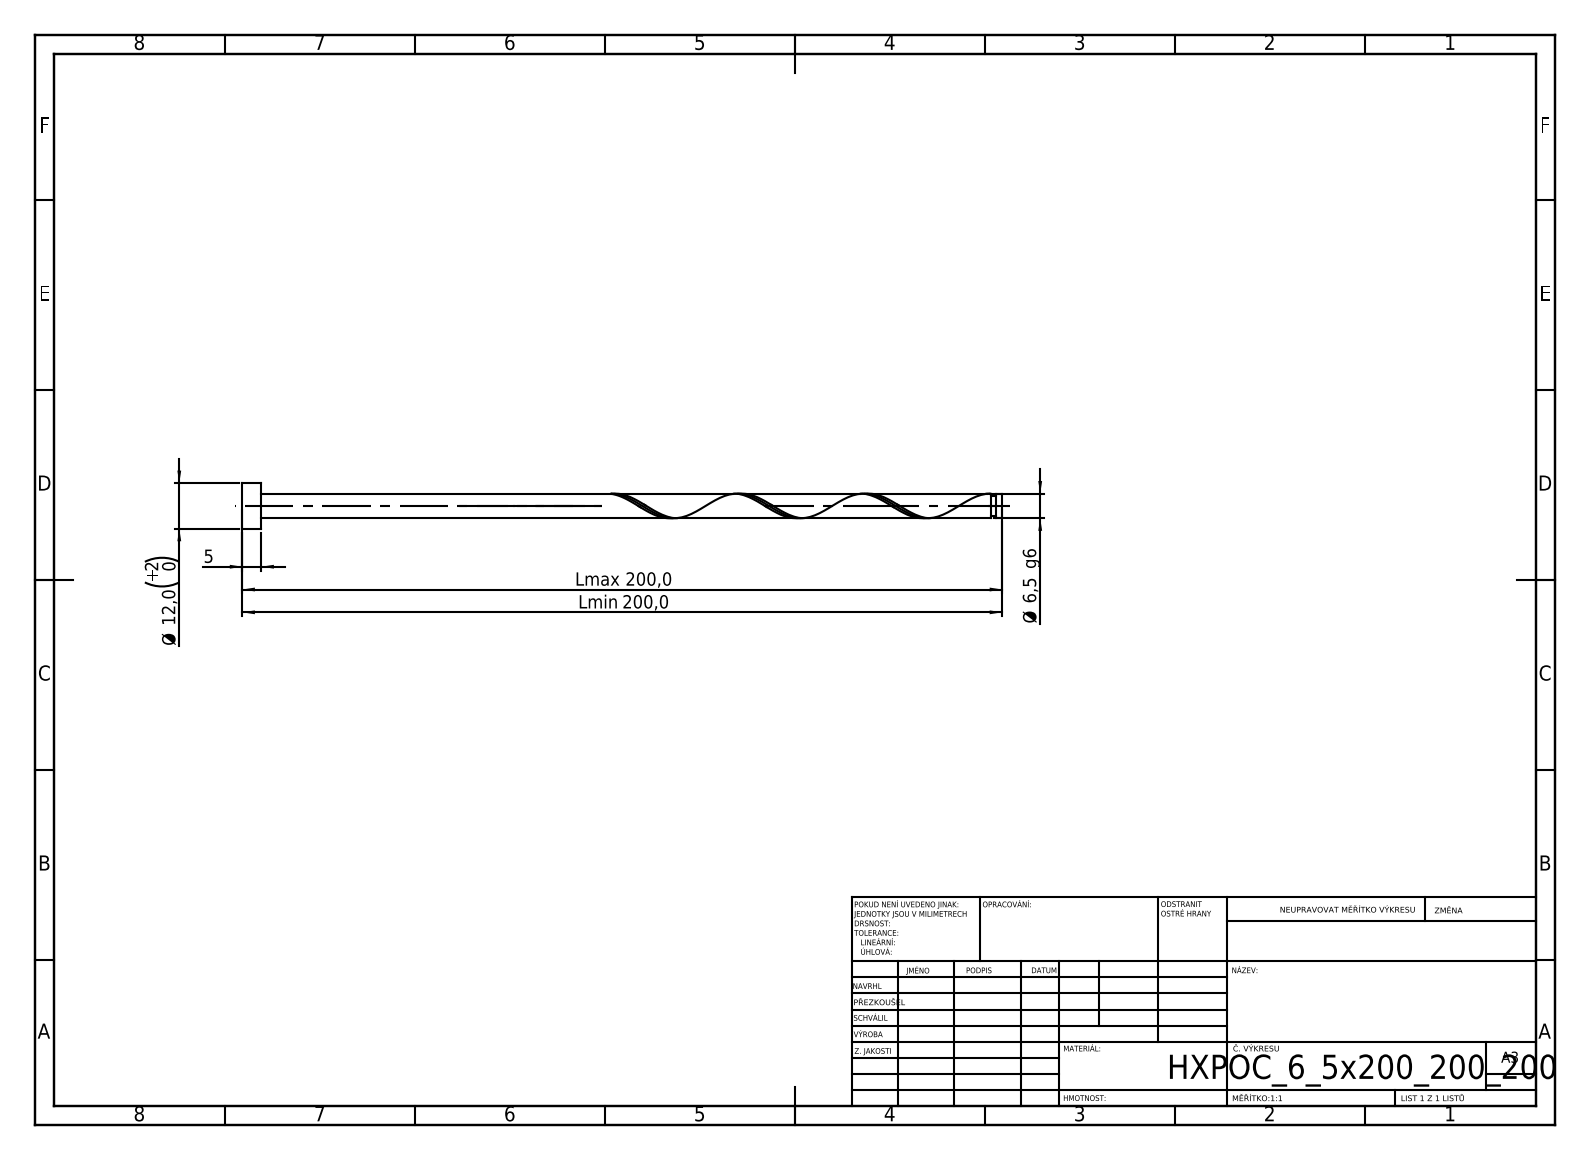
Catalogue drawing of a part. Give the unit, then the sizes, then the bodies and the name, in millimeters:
Units: millimetres
Overall size (bounding box): 200 × 12 × 12
Round bosses / shafts (diameter × count): ⌀12 ×1, ⌀6.5 ×1, ⌀5.2 ×1
Main face-to-face distances: 5, 200, 195, 198.23, 193.23, 1.77, 196.93, 191.93, 1.3, 3.07
Volume: 6 957 mm³ · Surface area: 4 492 mm²
Bodies: 1 solid, 21 faces (6 planar, 14 cylindrical, 1 other)
STEP written by: SolidWorks 2019 (CONFIG_CONTROL_DESIGN)
